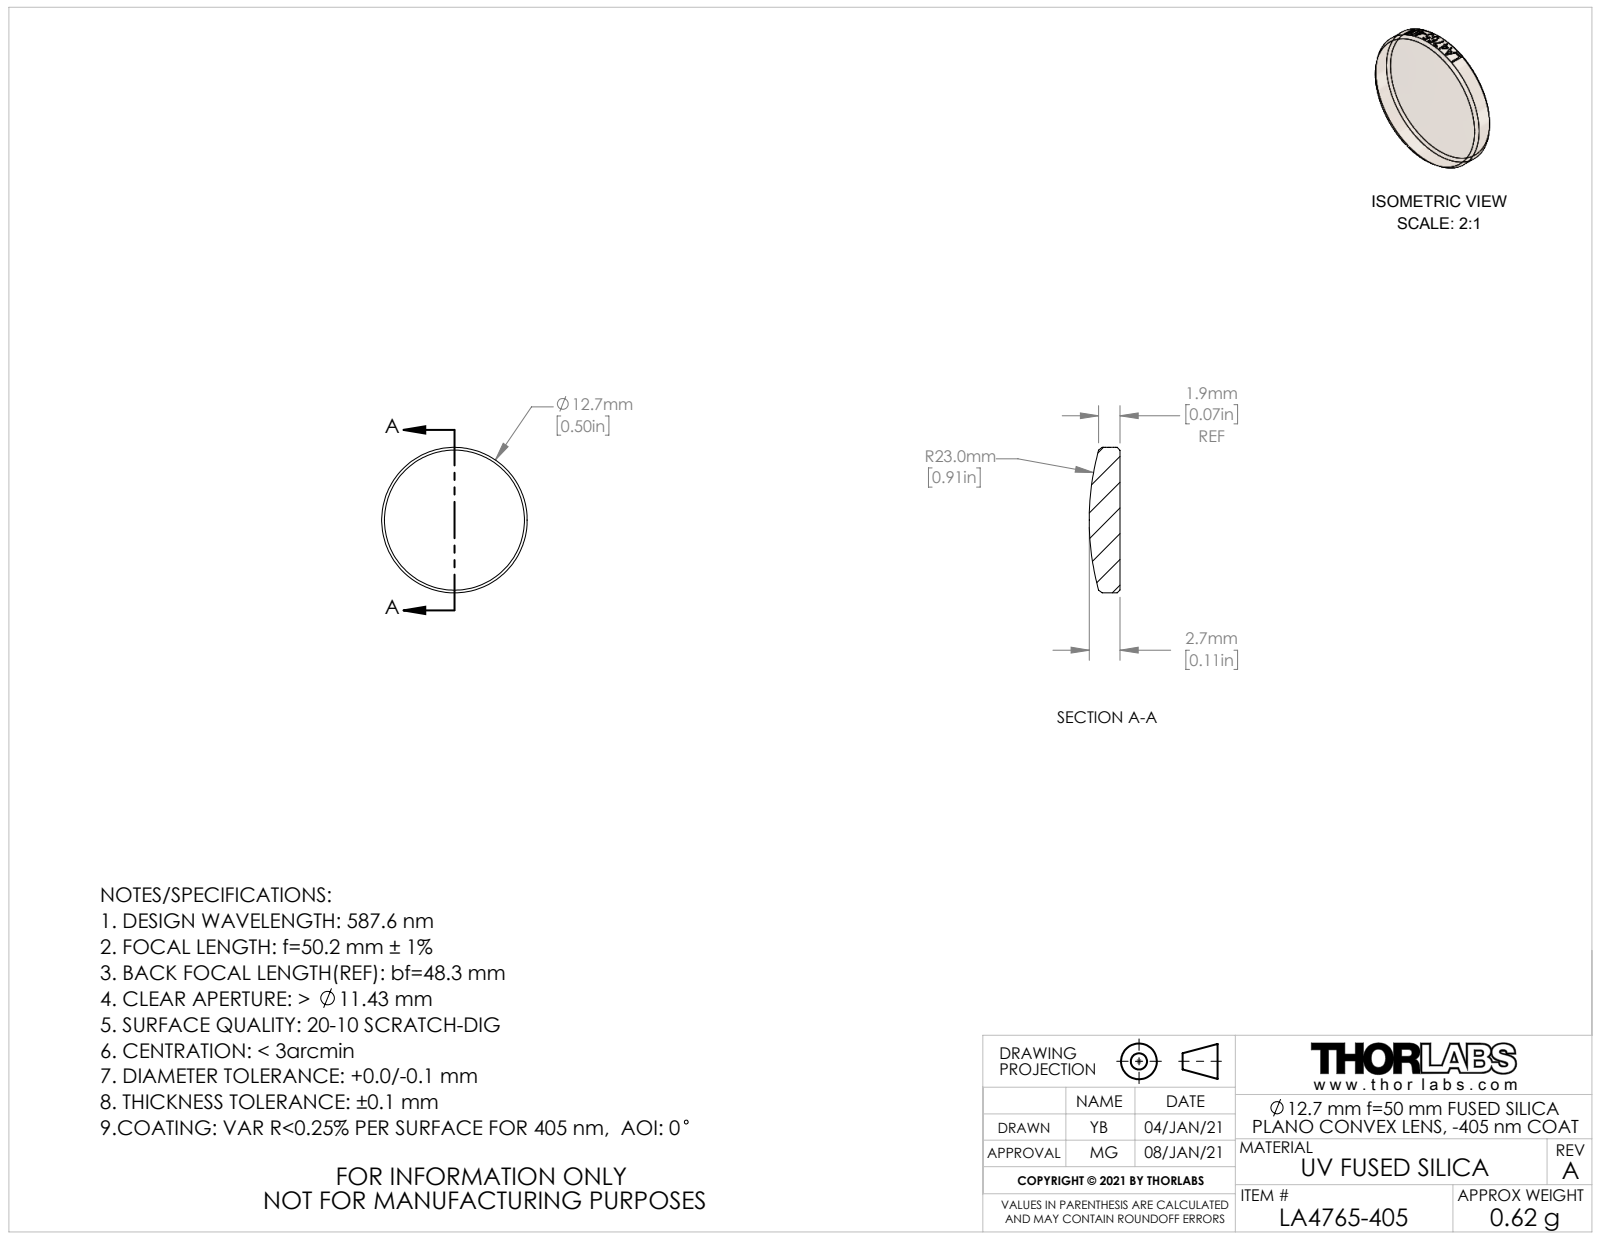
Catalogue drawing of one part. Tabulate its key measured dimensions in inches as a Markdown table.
| quantity | value |
| --- | --- |
| part name | CTN016813-E0W; CTN016833 |
| STEP written by | SolidWorks 2018 (AUTOMOTIVE_DESIGN) |
| units | inches |
| bodies | 1 solid, 24 faces (1 planar, 17 cylindrical, 6 other) |
| overall size | 0.5 × 0.5 × 0.106 |
| volume | 0.017 in³ |
| surface area | 0.492 in² |
| round bosses / shafts (diameter × count) | 0.5 × 1 |
